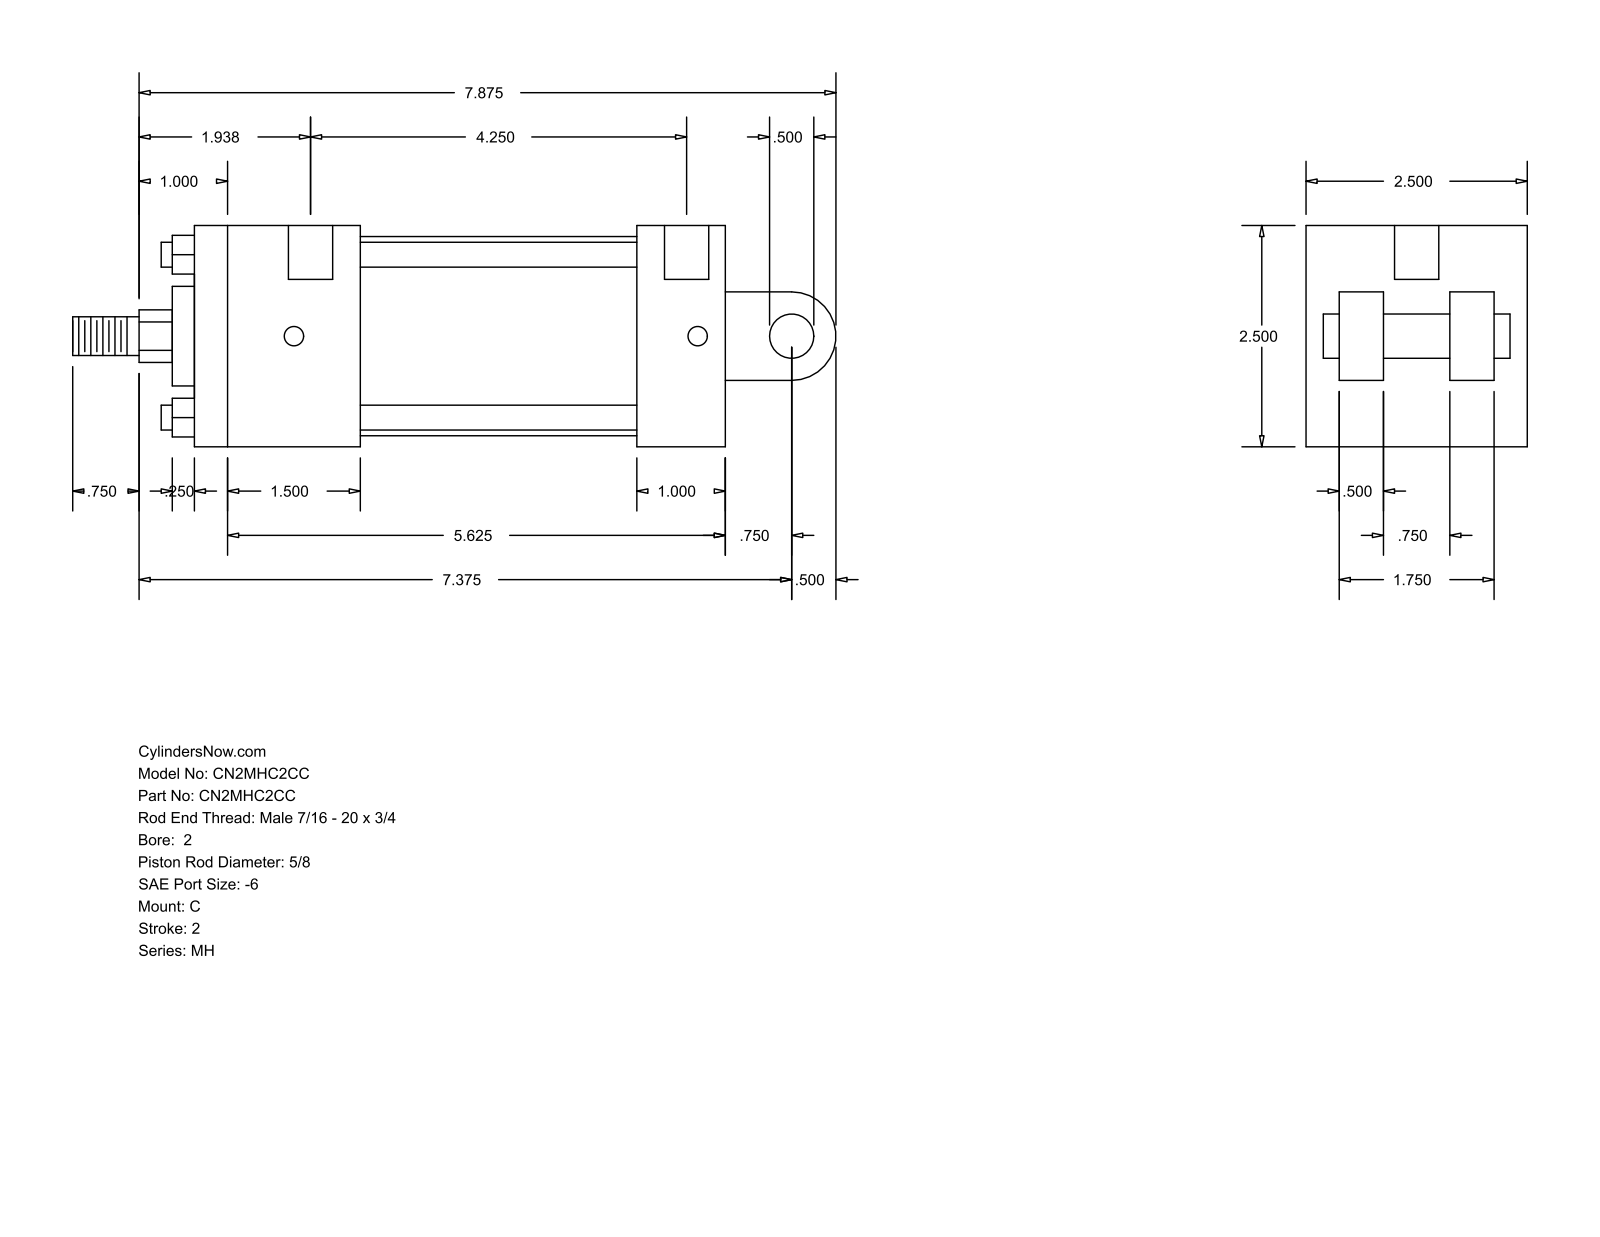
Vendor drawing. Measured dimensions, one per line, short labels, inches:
name: MH_C__0200_0.625
written by: GSSL Pune (CONFIG_CONTROL_DESIGN)
unit: in
bodies: 0 solids, 99 faces (70 planar, 29 cylindrical, 0 other)
size: 8.625 × 2.5 × 2.5
holes: 4× ⌀0.219, 2× ⌀0.5
bosses: 4× ⌀0.281, 1× ⌀2.25, 1× ⌀1.125, 1× ⌀0.625, 1× ⌀0.5, 1× ⌀0.437
rounds: 1× R0.297, 1× R0.5
face distances: 2.5, 6, 1, 0.5, 1.875, 5, 3.125, 4.125, 0.75, 0.375
hole spacings: 4.563, 0.125, 0.187, 4.25, 4.375, 4.437
